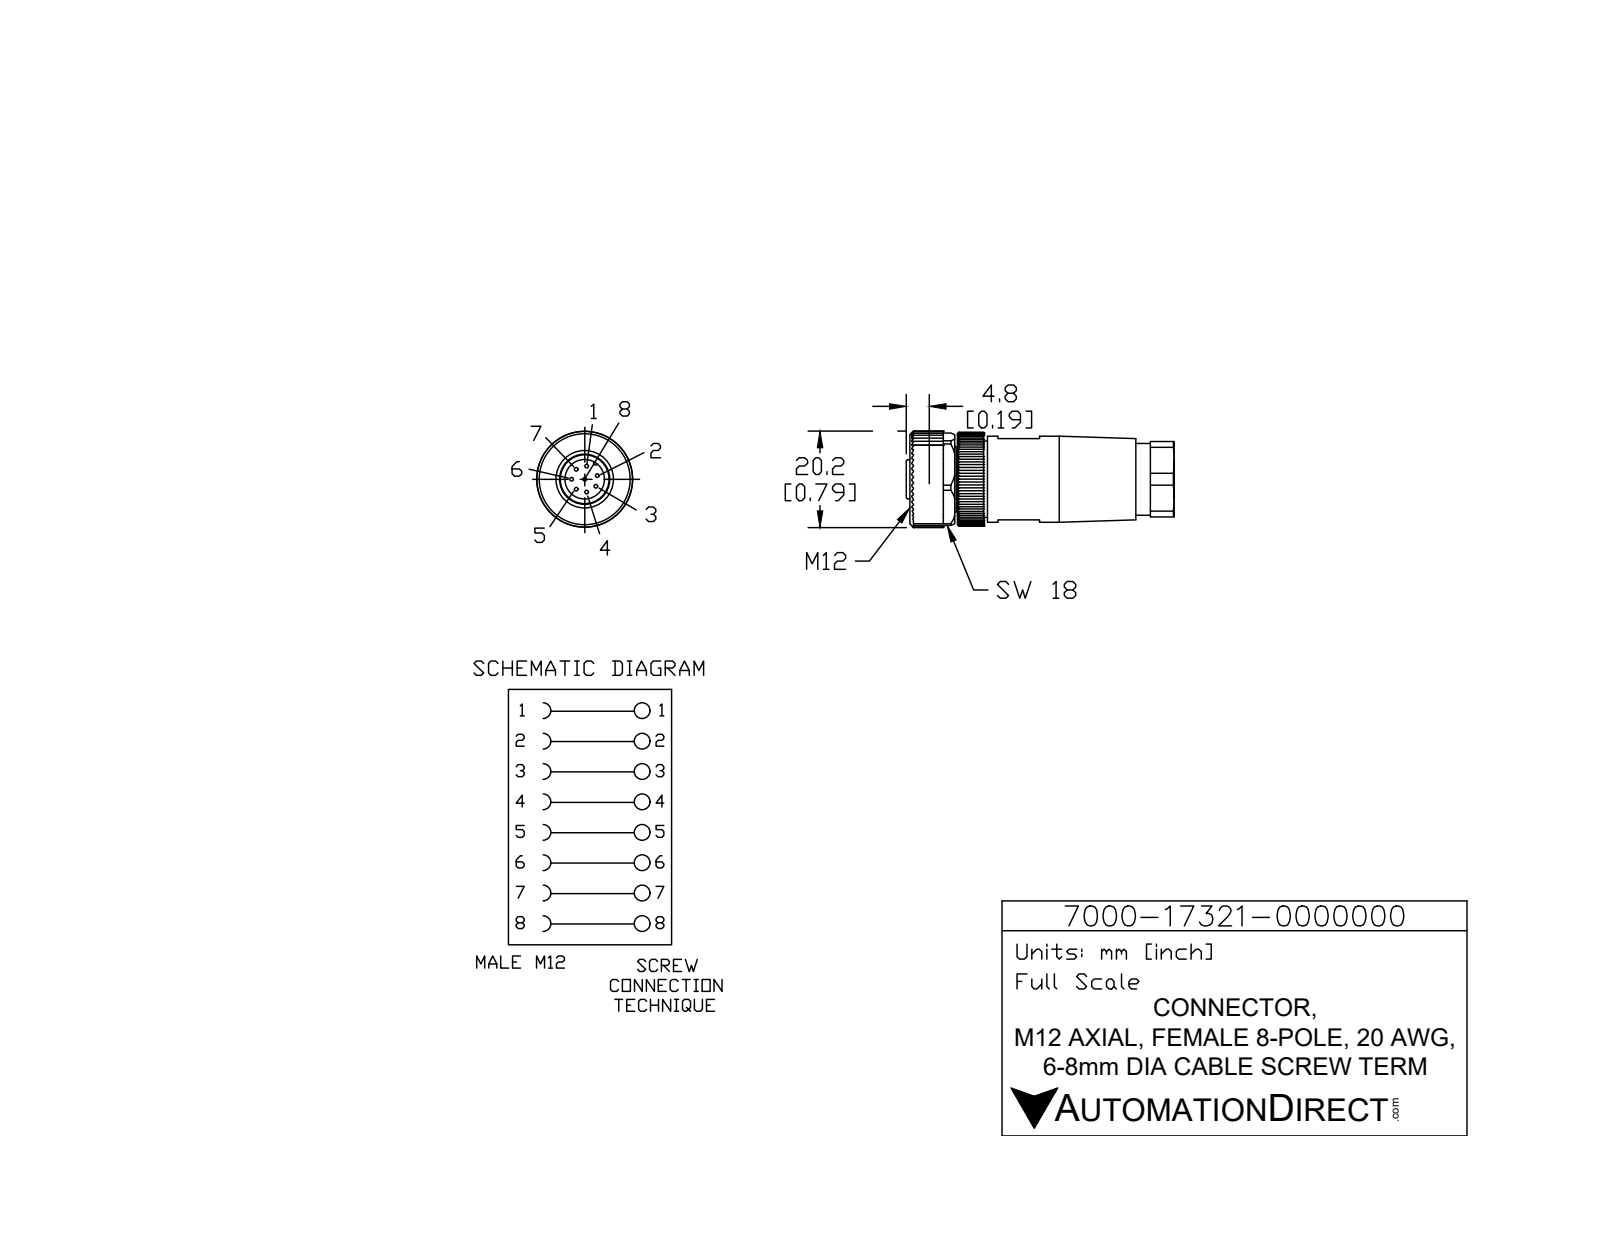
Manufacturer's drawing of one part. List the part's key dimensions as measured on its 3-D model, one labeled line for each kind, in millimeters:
Part name (STEP PRODUCT): 7000-17321-0000000
STEP written by: SolidWorks 2017 (AUTOMOTIVE_DESIGN)
Units: millimetres
Bodies: 1 solid, 86 faces (35 planar, 43 cylindrical, 8 other)
Overall size (bounding box): 54 × 20 × 20
Volume: 8 600 mm³ · Surface area: 6 363 mm²
Round holes (diameter × count): ⌀0.8 ×8, ⌀10 ×1, ⌀14 ×1
Round bosses / shafts (diameter × count): ⌀20 ×1, ⌀20 ×1, ⌀18 ×1, ⌀15 ×1, ⌀12 ×1, ⌀8 ×1
Partial cylindrical surfaces — rounded edges, fillets, slot ends (radius × count): R0.7 ×1, R8.5 ×1
Main face-to-face distances: 5.8, 14.8, 9.3, 5.5, 9, 52.5, 43.5, 43.2, 37.7, 30
Hole centre spacings: 2.7, 2.3, 4.1, 5.3, 2.3, 2.8, 4.2, 2.3
